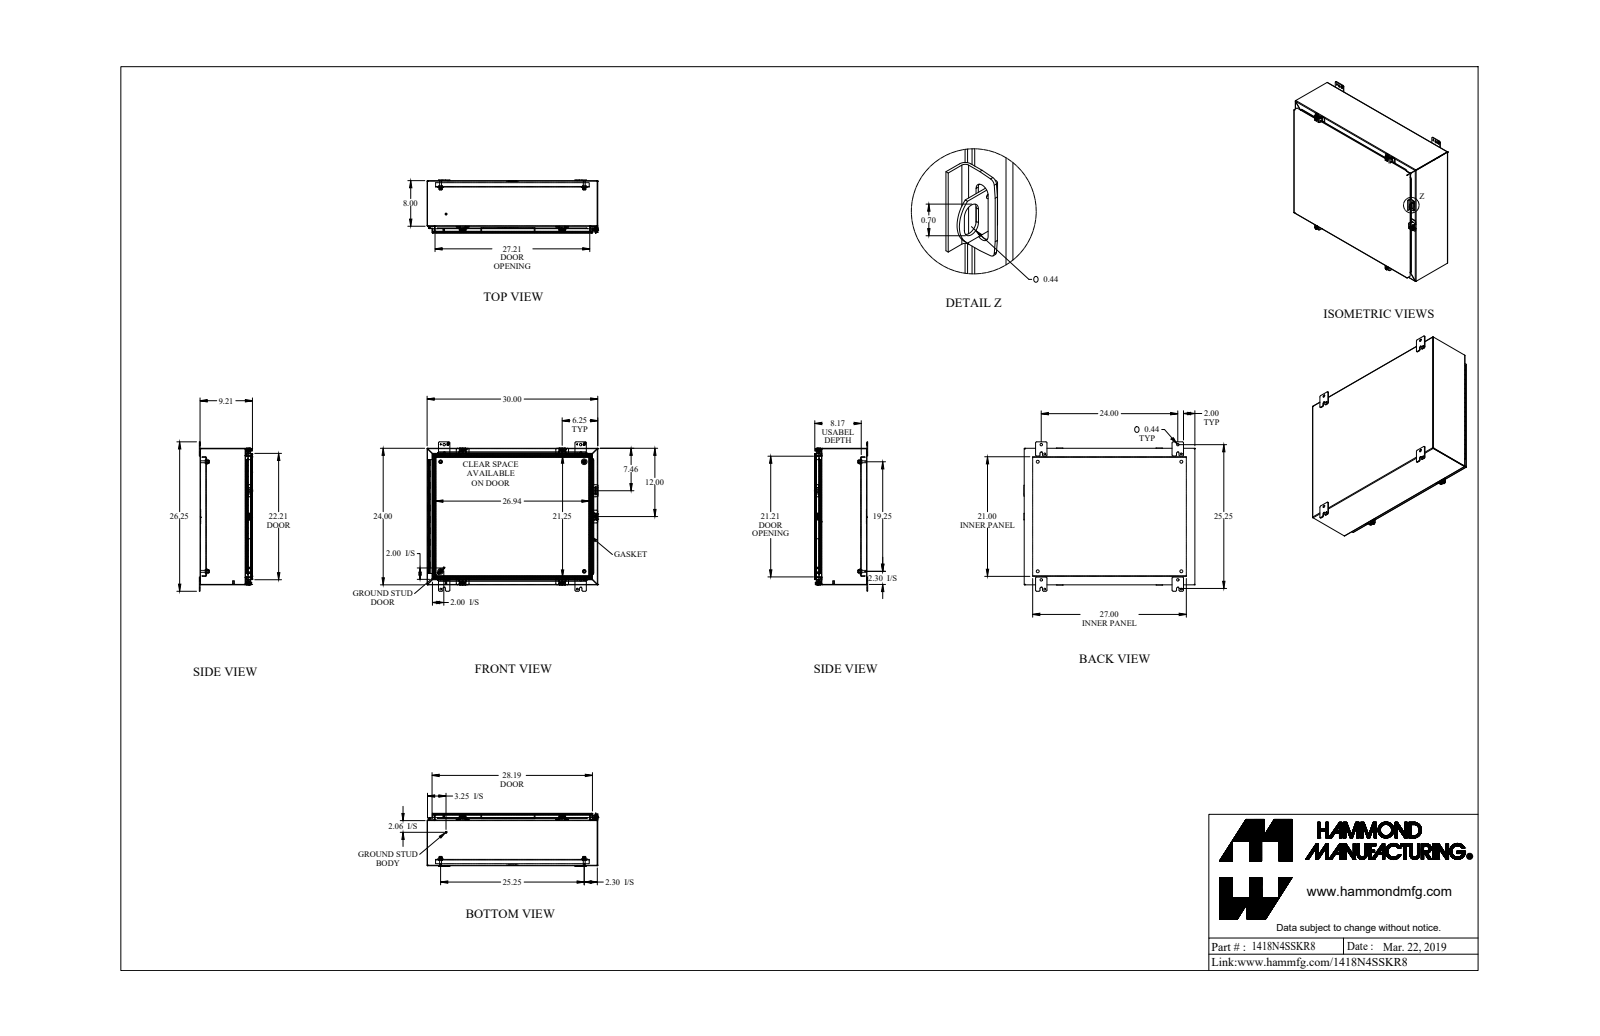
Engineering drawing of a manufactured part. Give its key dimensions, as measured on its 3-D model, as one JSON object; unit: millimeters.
{"part_name": "1418N4SSKR8_Default", "step_written_by": "SolidWorks 2019 (CONFIG_CONTROL_DESIGN)", "units": "millimeters", "bodies": {"solids": 43, "faces": 1634, "planar": 1013, "cylindrical": 526, "other": 95}, "overall_size": [763.6, 666.8, 238.1], "volume_mm3": 4216000, "surface_area_mm2": 4349000, "round_holes": [[5.4, 5], [6.7, 5], [9.5, 5], [8, 4], [11.1, 4], [12.7, 4], [7.8, 2], [11.3, 2], [3.2, 1], [4.7, 1]], "round_bosses_or_shafts": [[12.7, 5], [9.9, 5], [6.2, 5], [16.5, 4], [9.5, 4], [8.4, 4], [25.4, 2], [8, 2]], "partial_cylinders_radius": [[4.8, 26], [0.9, 24], [2.7, 24], [6.4, 24], [1.2, 21], [3.6, 21], [3.2, 10], [3.6, 10]], "face_to_face_distances": [1.8, 1.8, 230.3, 232.1, 232.1, 233.9, 2.4, 23.8, 25.6, 205.9], "hole_center_spacings": [527.3, 112.3, 545.6, 551.8, 609.6, 767.8, 857.6, 489]}
